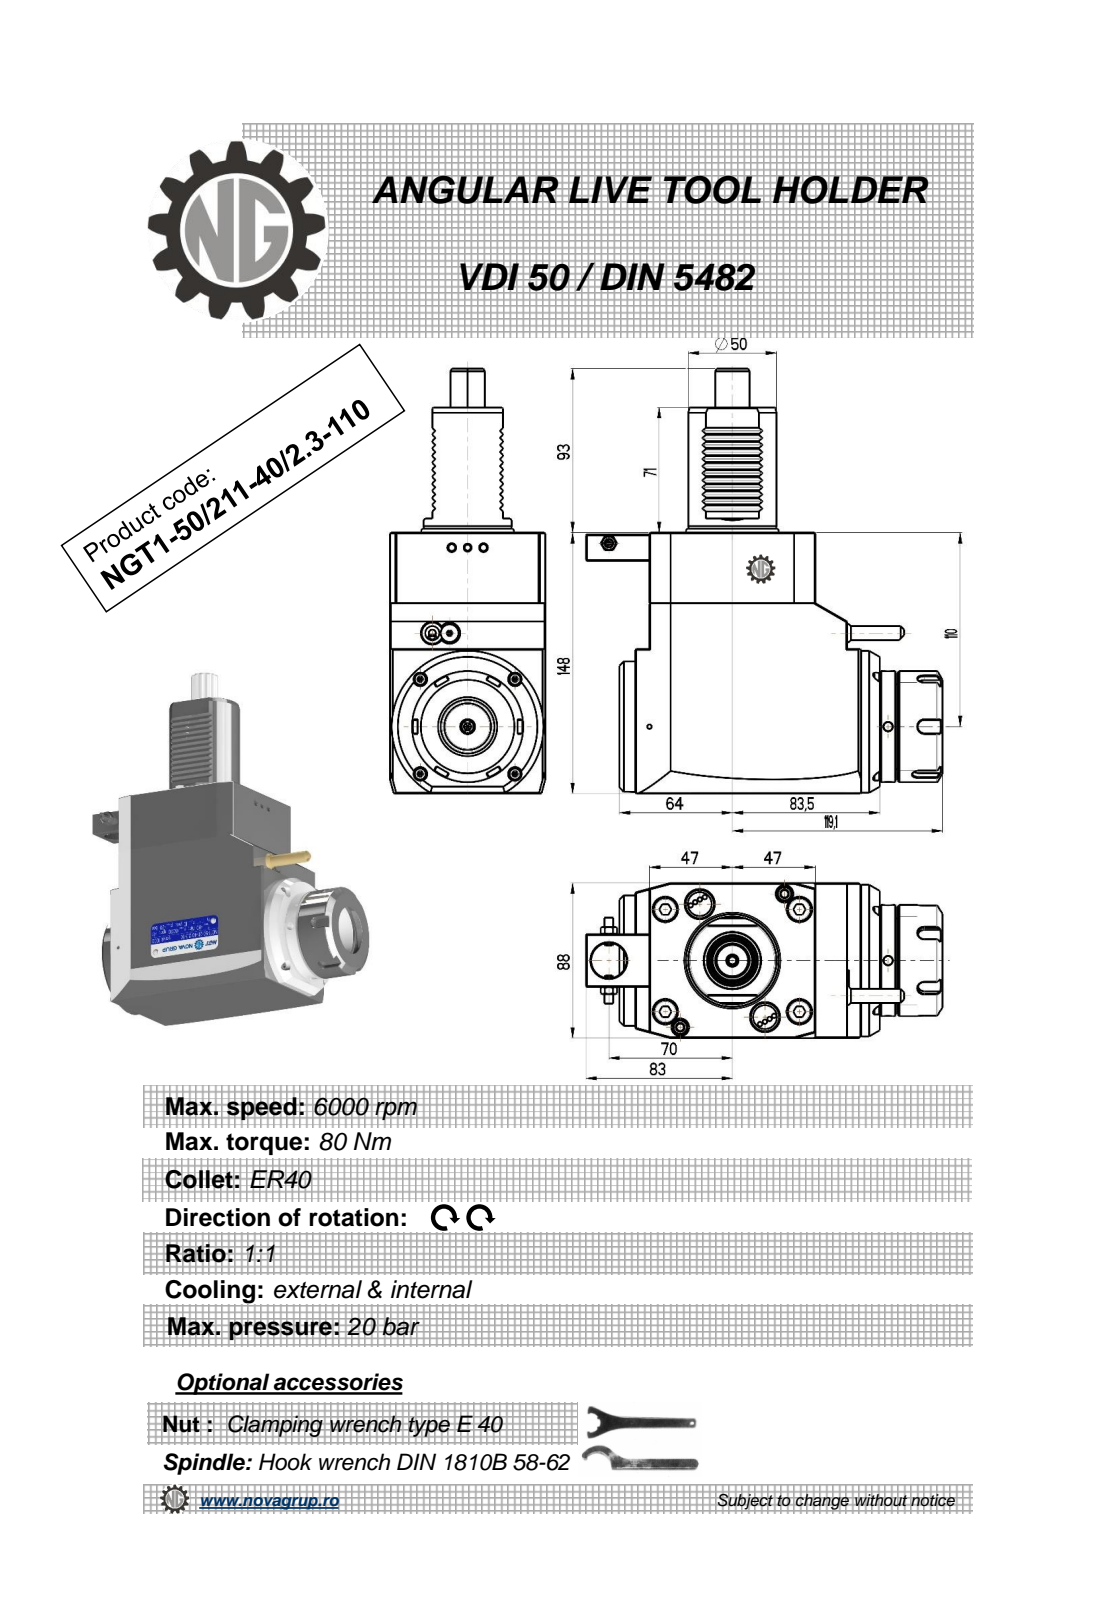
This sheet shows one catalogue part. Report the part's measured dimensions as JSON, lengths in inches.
{"part_name": "NGT1_50_211_40_1_3_110", "step_written_by": "PRO/ENGINEER BY PARAMETRIC TECHNOLOGY CORPORATION, 2010280 (CONFIG_CONTROL_DESIGN)", "units": "inches", "bodies": {"solids": 1, "faces": 540, "planar": 243, "cylindrical": 153, "other": 144}, "overall_size": [9.488, 7.957, 3.465], "volume_in3": 111.2, "surface_area_in2": 178.8, "round_holes": [[0.197, 3], [0.118, 1], [0.165, 1], [0.209, 1], [0.374, 1], [0.787, 1], [1.319, 1]], "round_bosses_or_shafts": [[3.386, 1], [2.913, 1], [2.48, 1], [2.008, 1], [1.969, 1], [0.394, 1], [0.353, 1], [0.315, 1]], "partial_cylinders_radius": [[0.012, 24], [0.131, 24], [0.01, 12], [0.008, 6], [0.148, 5], [0.098, 1], [0.325, 1], [0.384, 1]], "face_to_face_distances": [3.465, 5.827, 5.807, 0.669, 0.315, 3.701, 4.37, 0.354, 5.138, 1.437], "hole_center_spacings": [2.065, 2.23, 2.756, 3.474, 3.996, 6.23]}
